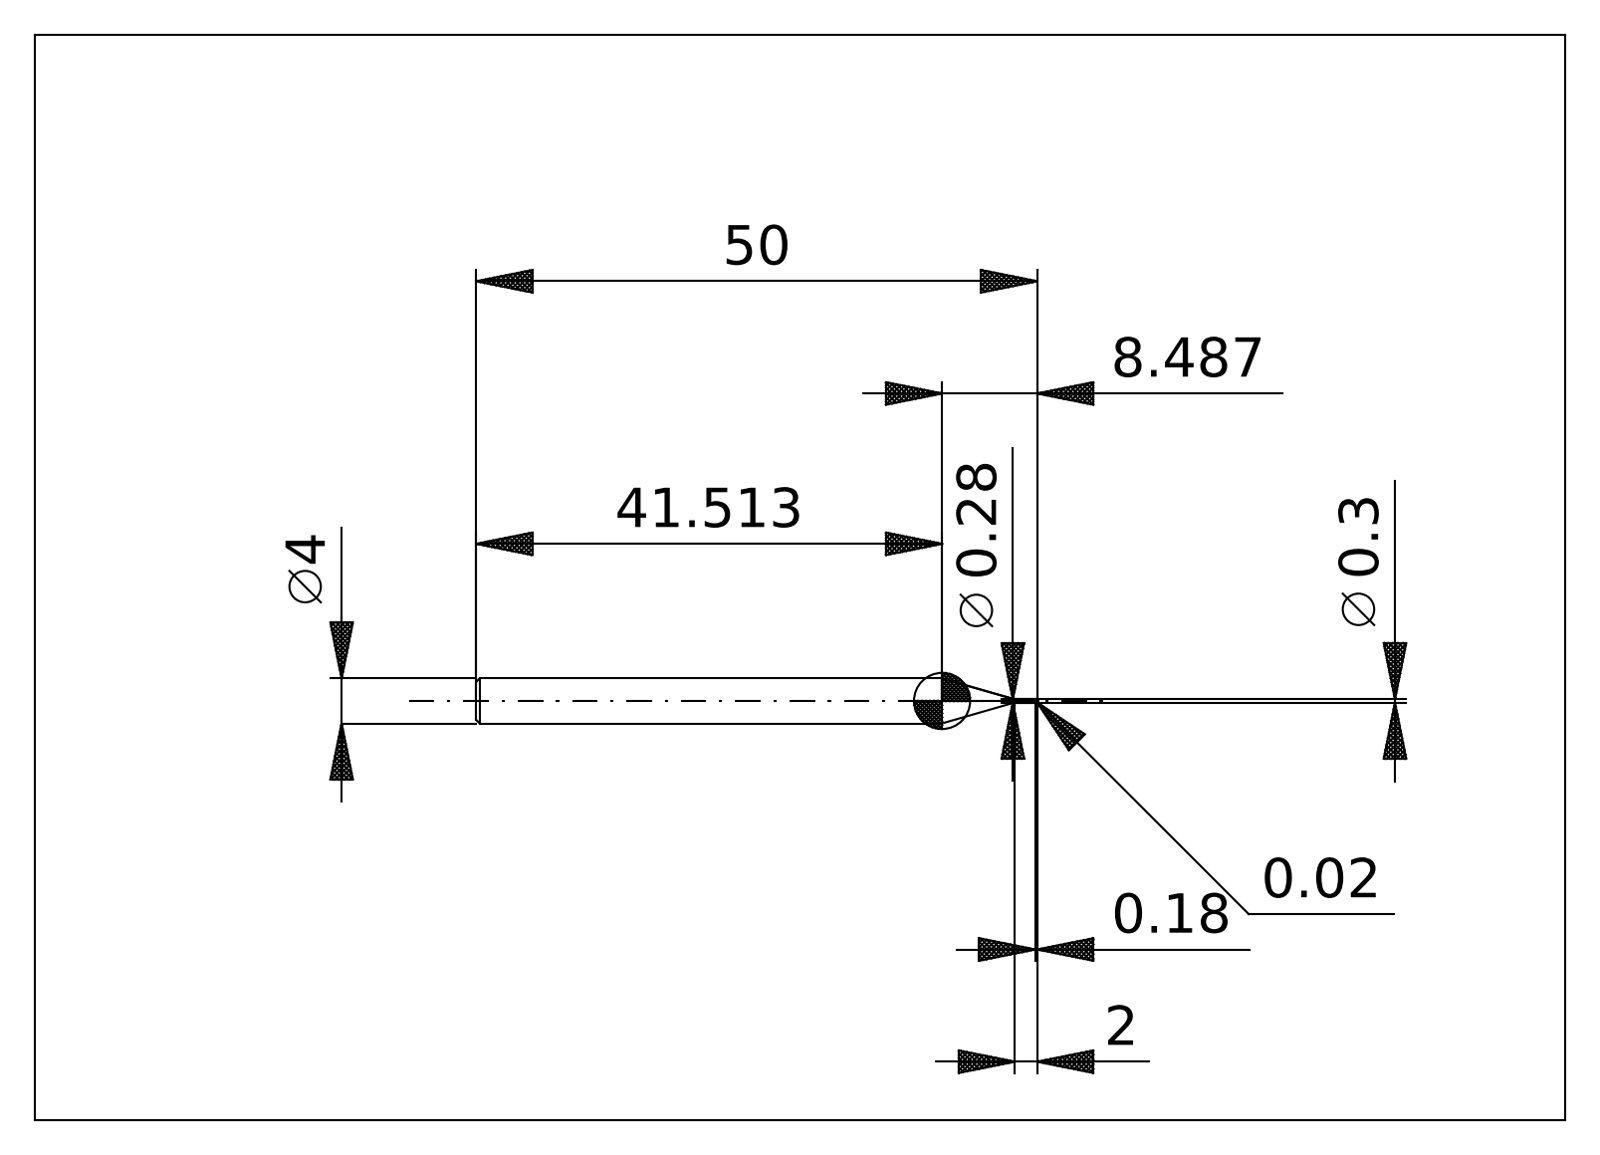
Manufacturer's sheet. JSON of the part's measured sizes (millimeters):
{"step_written_by": "ACIS (automotive_design)", "units": "millimeters", "bodies": {"solids": 2, "faces": 26, "planar": 6, "cylindrical": 8, "other": 12}, "overall_size": [50, 4, 4], "volume_mm3": 550, "surface_area_mm2": 579, "round_bosses_or_shafts": [[4, 1], [0.28, 1]], "face_to_face_distances": [50, 49.96, 49.82, 8.49, 8.45, 8.31, 41.51]}
